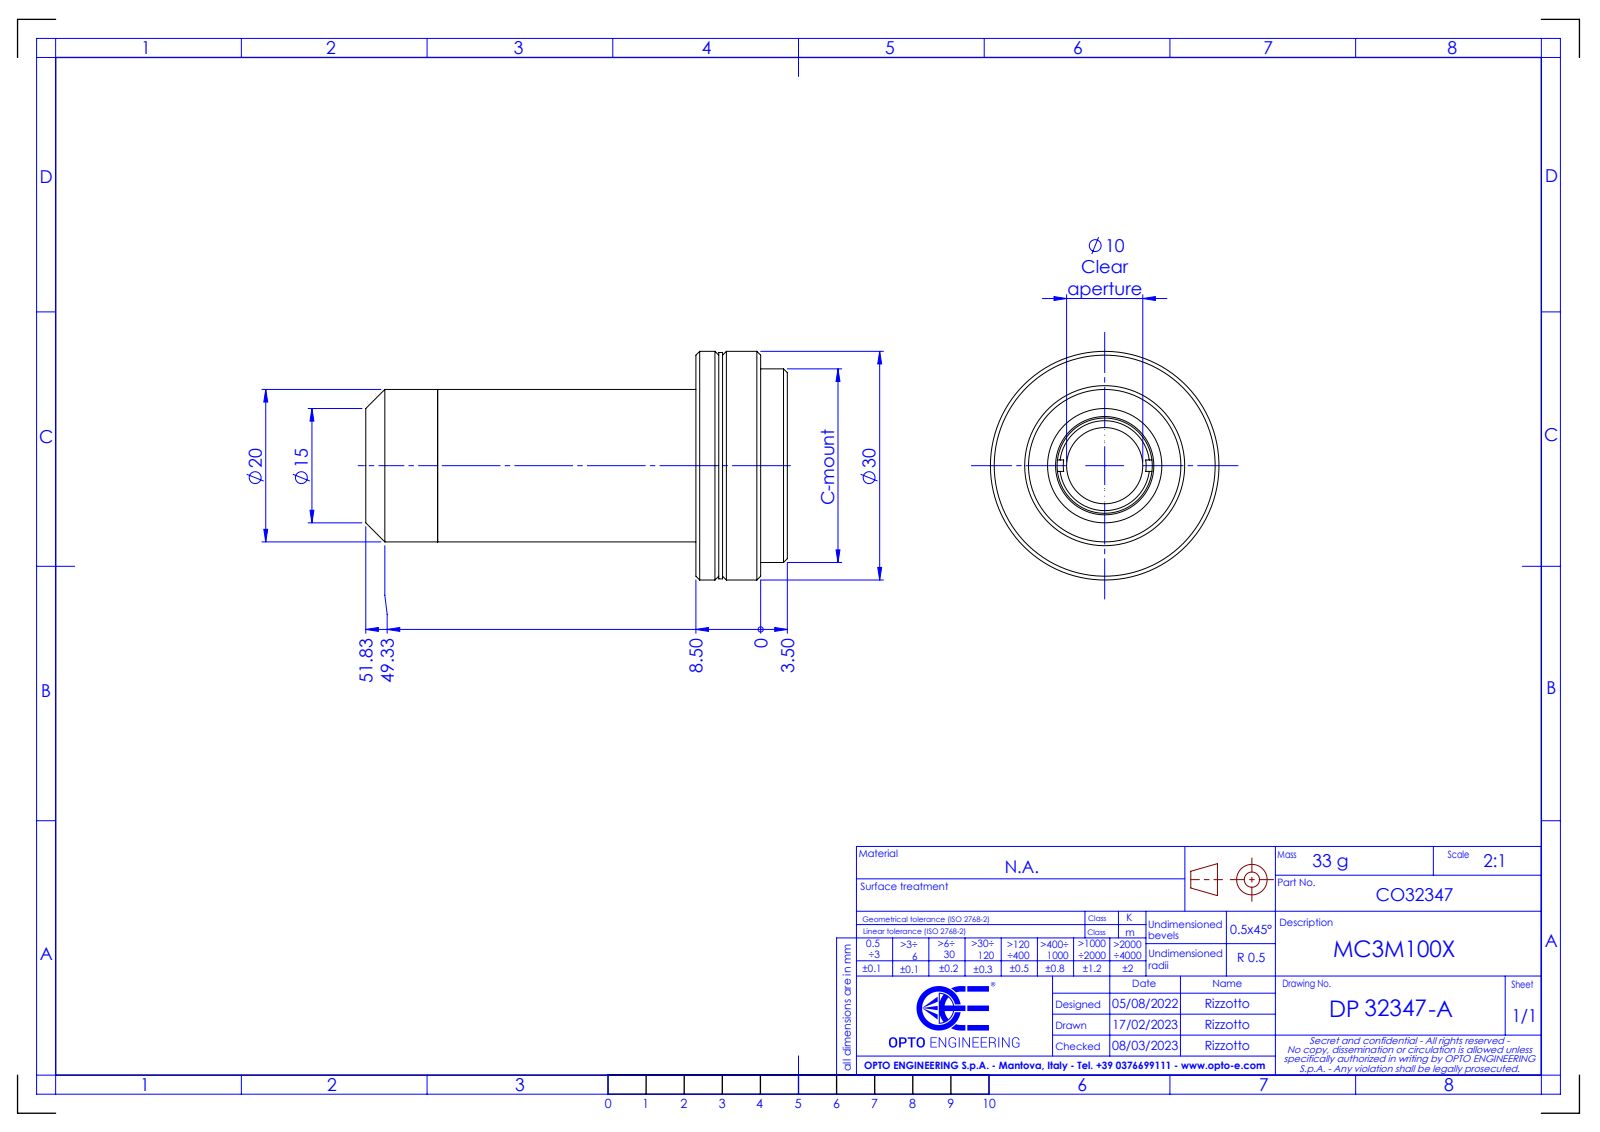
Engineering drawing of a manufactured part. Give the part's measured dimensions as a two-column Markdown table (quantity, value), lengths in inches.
| quantity | value |
| --- | --- |
| part name | DP32347-A_MC3M100X |
| STEP written by | SolidWorks 2021 (CONFIG_CONTROL_DESIGN) |
| units | inches |
| bodies | 0 solids, 65 faces (17 planar, 22 cylindrical, 26 other) |
| overall size | 2.178 × 1.181 × 1.181 |
| round holes (diameter × count) | 0.394 × 1, 0.492 × 1, 0.689 × 1, 0.709 × 1 |
| round bosses / shafts (diameter × count) | 1.181 × 1, 1.169 × 1, 1 × 1, 0.787 × 1 |
| main face-to-face distances | 0.335, 0.138, 0.197, 0.118, 0.02, 0.217, 0.472, 0.354, 1.335, 1.453 |
